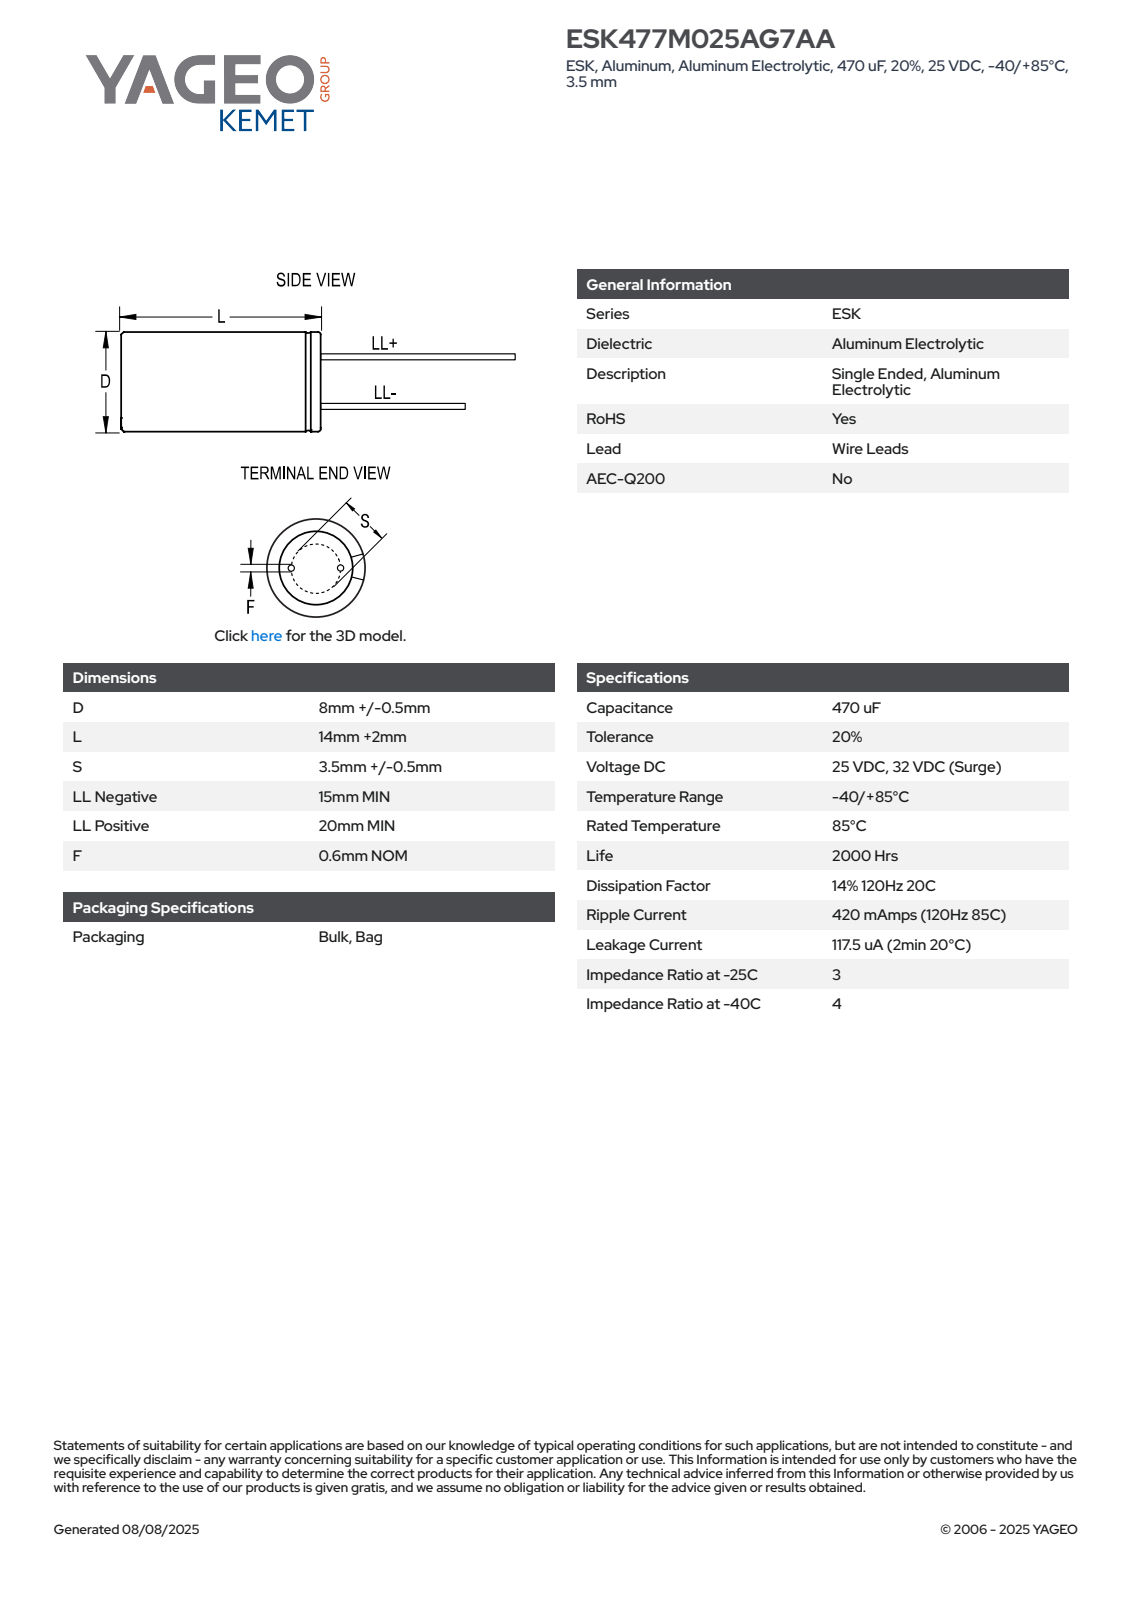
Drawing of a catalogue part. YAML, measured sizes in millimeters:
part_name: "CAR_KLP_8X14_D8.5L16S3.5F0.6"
step_written_by: "SolidWorks 2014 (AUTOMOTIVE_DESIGN)"
units: millimeters
bodies: {solids: 4, faces: 75, planar: 61, cylindrical: 8, other: 6}
overall_size: [36.01, 8.5, 8.5]
volume: 911
surface_area: 622
round_bosses_or_shafts:
  - {diameter: 0.6, count: 2}
  - {diameter: 8.5, count: 1}
face_to_face_distances: [16, 16.01, 31.01, 36.01, 31, 36, 15, 20, 5, 1.15]
